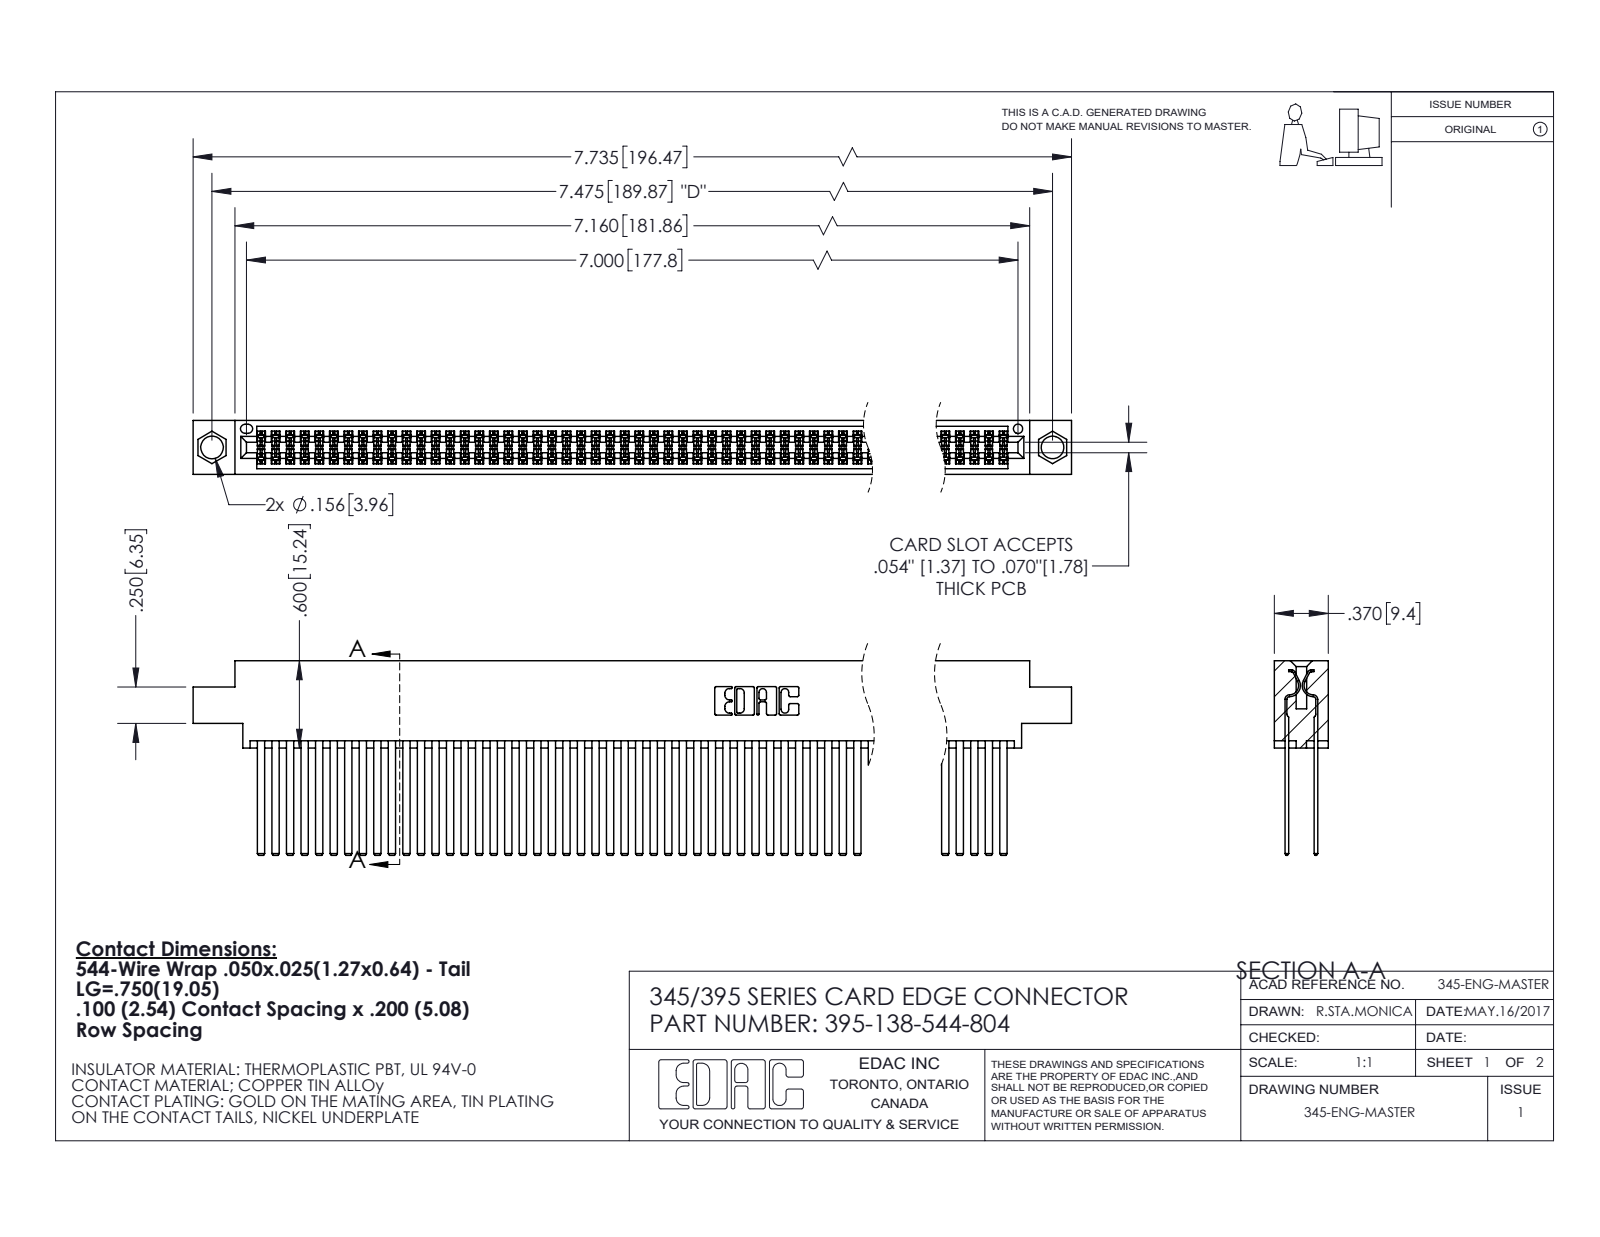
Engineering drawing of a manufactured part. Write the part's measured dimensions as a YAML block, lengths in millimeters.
part_name: "345-292-001_345-293-144; 345 Part_0.170 Offset - 0.156 Dia-TI; 395-138-544-804"
step_written_by: "SolidWorks 2020 (CONFIG_CONTROL_DESIGN)"
units: millimeters
bodies: {solids: 139, faces: 6216, planar: 4100, cylindrical: 2116, other: 0}
overall_size: [196.5, 34, 9.4]
volume: 21060
surface_area: 37300
round_holes:
  - {diameter: 4, count: 2}
  - {diameter: 1.6, count: 1}
partial_cylinders:
  - {radius: 0.2, count: 207}
  - {radius: 0.3, count: 22}
  - {radius: 0.2, count: 6}
  - {radius: 0.8, count: 6}
  - {radius: 0.7, count: 3}
  - {radius: 0.4, count: 2}
  - {radius: 0.5, count: 2}
  - {radius: 0.6, count: 2}
face_to_face_distances: [5.1, 0.6, 1.8, 2.5, 6.9, 7.6, 5.7, 4.4, 9.4, 3.8]
hole_center_spacings: [6.9, 183.9, 189.9]
